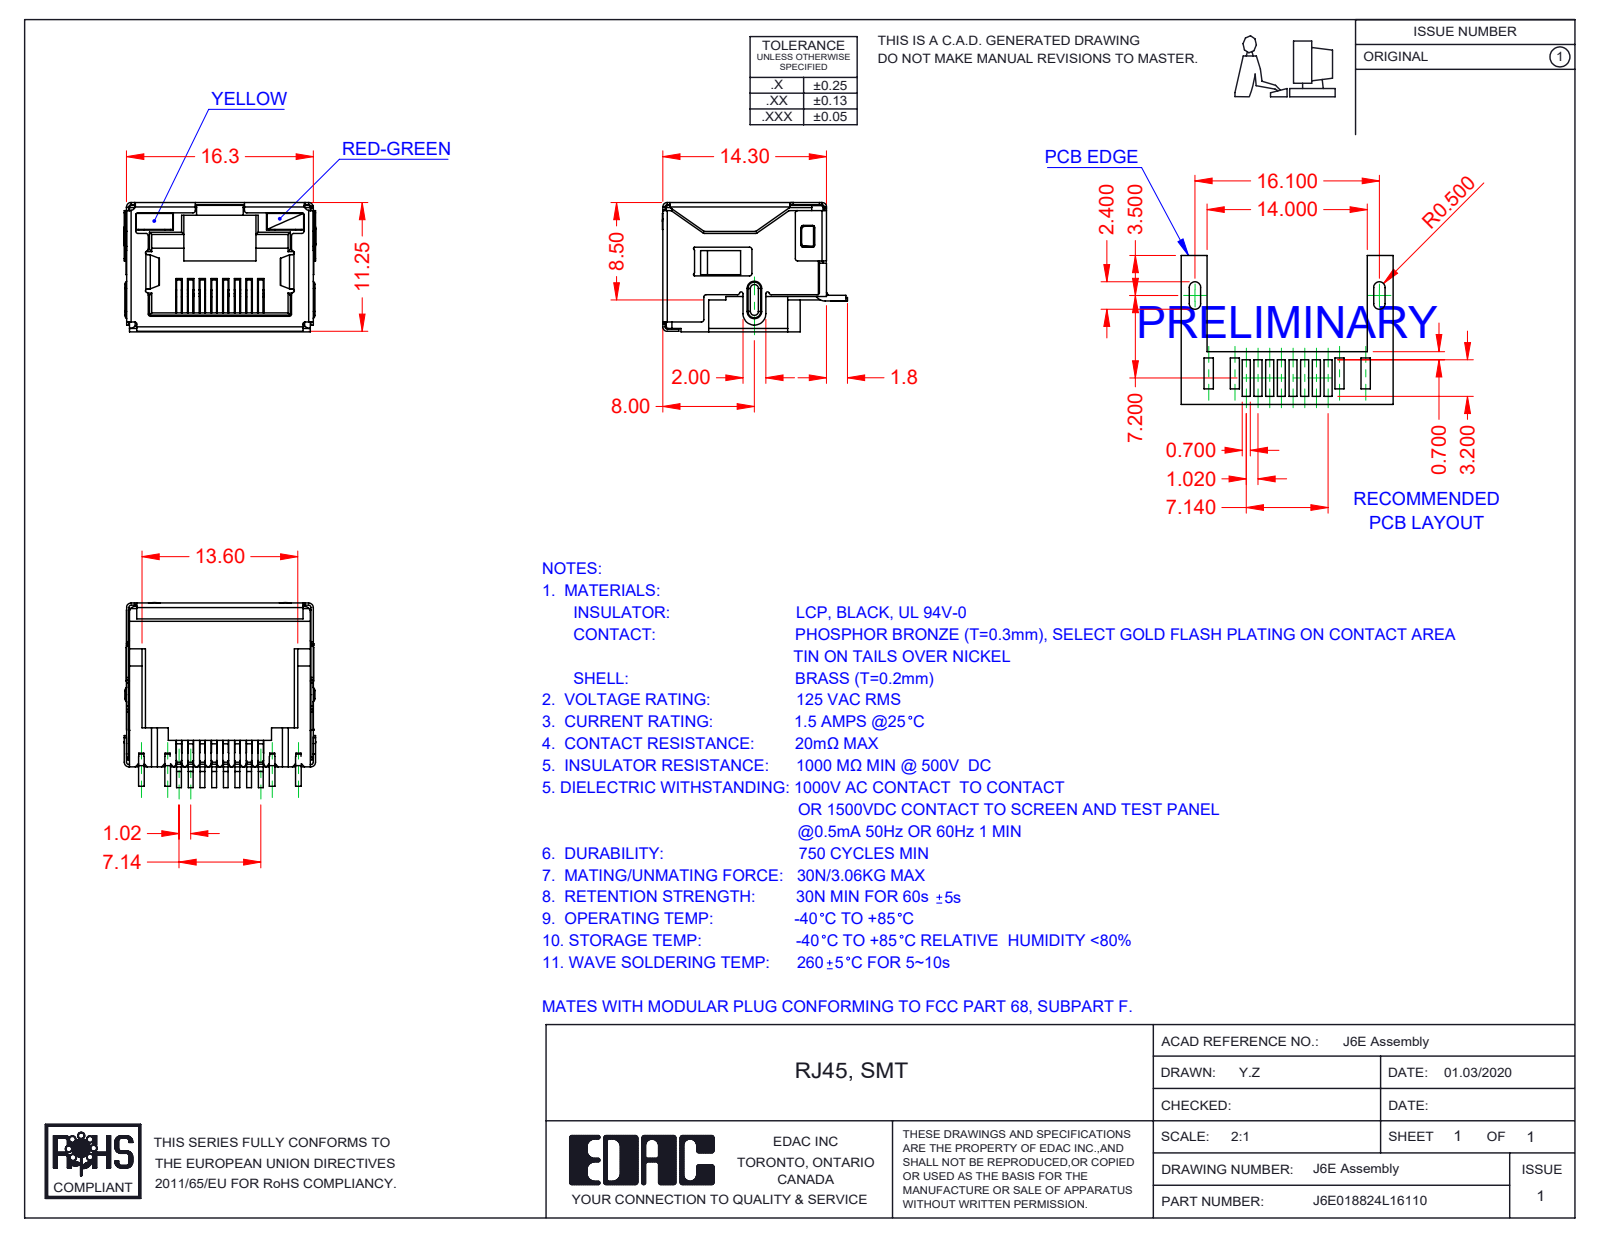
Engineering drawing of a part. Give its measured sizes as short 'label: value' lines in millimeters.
name: 6E LED RH_6-Red-Green; 6E LED LH_1-Yellow; 6E Insulator_LED; 6E Shield_LED (+2 more)
written by: SolidWorks 2016 (CONFIG_CONTROL_DESIGN)
unit: mm
bodies: 12 solids, 1498 faces (1099 planar, 349 cylindrical, 50 other)
size: 16.75 × 16.15 × 11.3
volume: 1 109 mm³; area: 4 045 mm²
rounds: 82× R0.2, 17× R0.25, 13× R0.4, 13× R0.5, 10× R0.1, 7× R0.15, 4× R0.3, 3× R1
face distances: 11.05, 16.05, 16.1, 15.85, 11.1, 11.3, 2.4, 0.7, 9.85, 0.49
